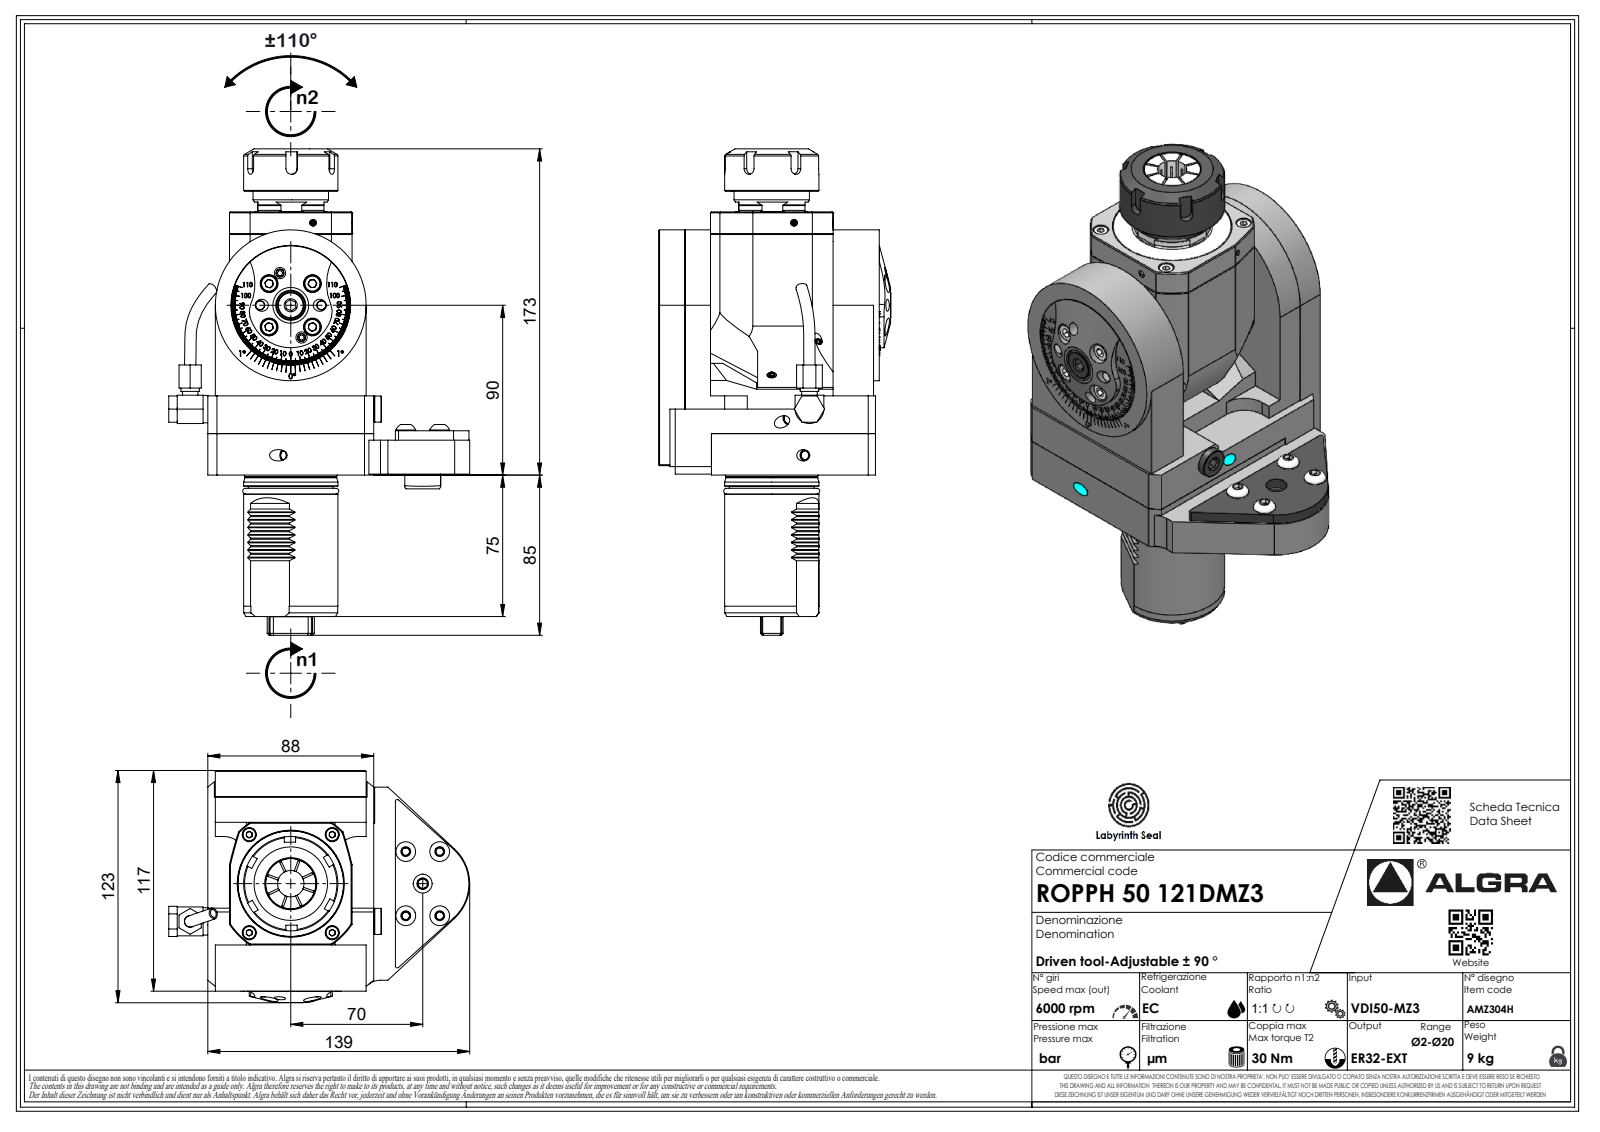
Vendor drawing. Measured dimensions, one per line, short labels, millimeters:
name: ROPPH50121DMZ3
written by: SolidWorks 2023 (AUTOMOTIVE_DESIGN)
unit: mm
bodies: 1 solid, 632 faces (404 planar, 104 cylindrical, 124 other)
size: 257.81 × 159.63 × 123
volume: 1 359 000 mm³; area: 118 021 mm²
holes: 1× ⌀2.1
bosses: 4× ⌀10.5, 1× ⌀80, 1× ⌀50, 1× ⌀49.85, 1× ⌀48.7, 1× ⌀45, 1× ⌀40, 1× ⌀20
rounds: 7× R0.3, 7× R0.33, 7× R0.52, 7× R3.7, 6× R2, 5× R3, 3× R10, 2× R1
face distances: 4, 11.5, 0.5, 65, 84, 117, 80, 22.5, 7.5, 76.5
